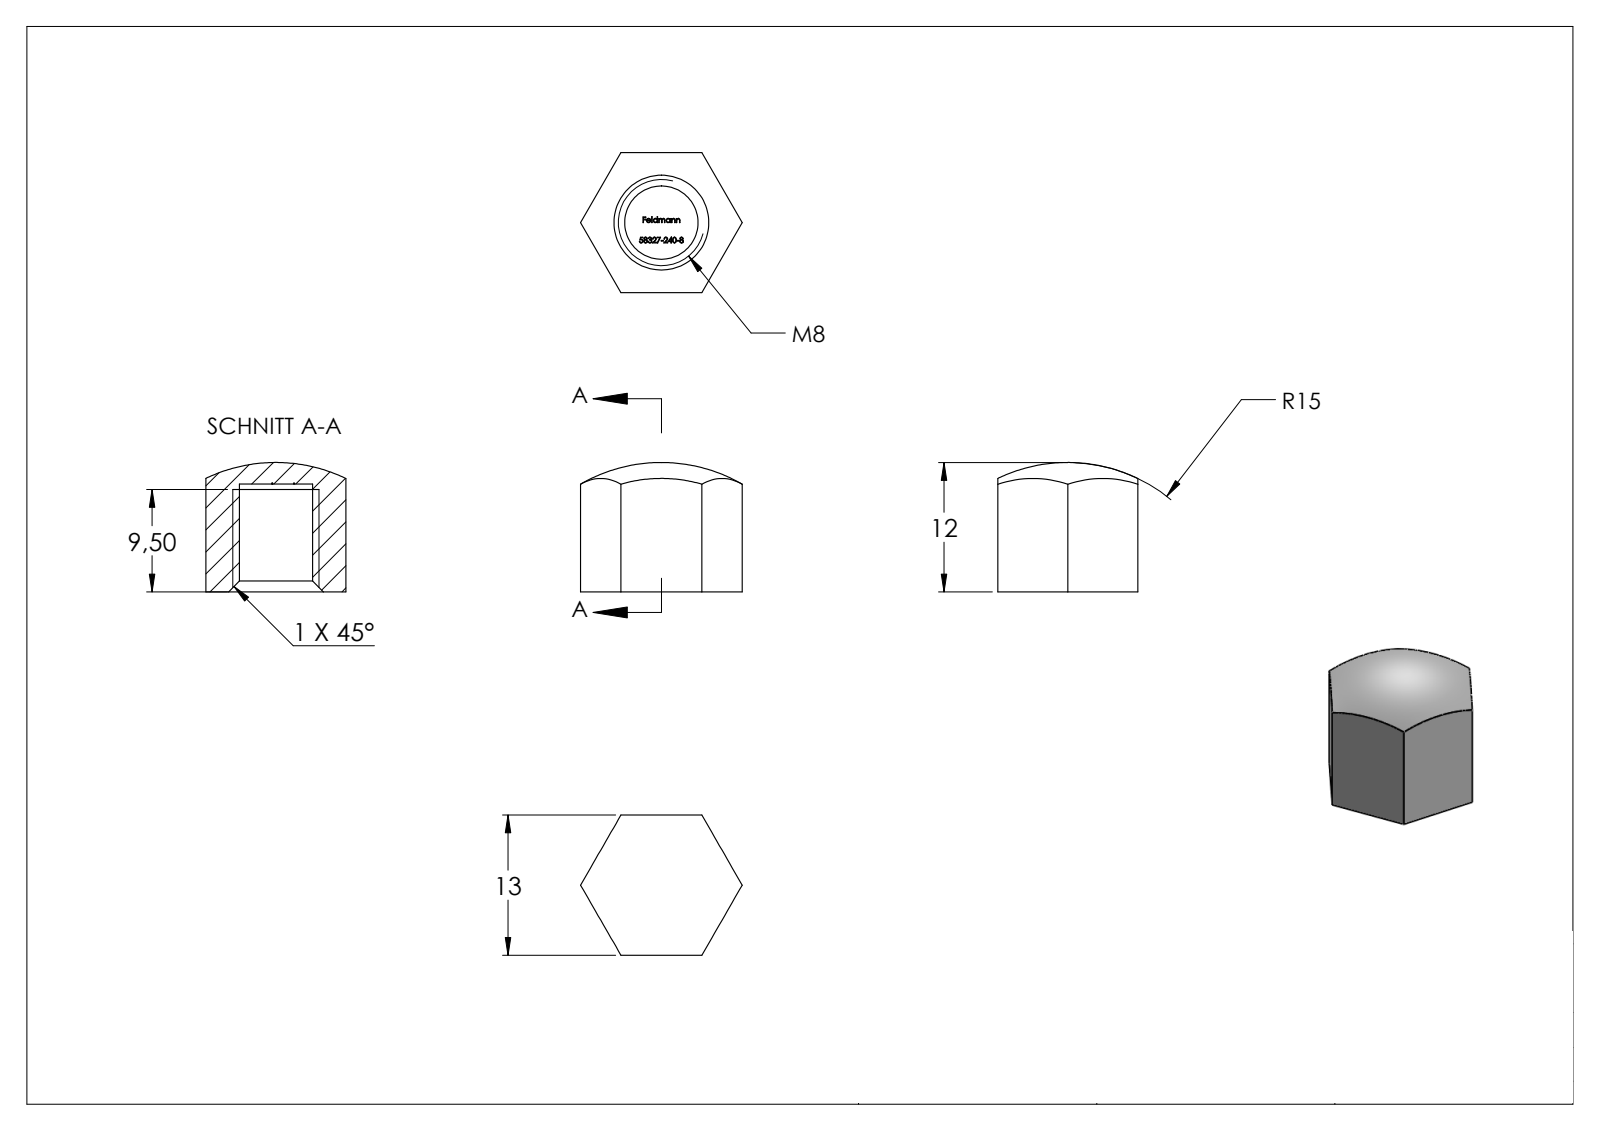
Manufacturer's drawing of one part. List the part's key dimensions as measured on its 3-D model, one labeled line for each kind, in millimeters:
Part name (STEP PRODUCT): 58327-240-8
STEP written by: SolidWorks 2018 (CONFIG_CONTROL_DESIGN)
Units: millimetres
Bodies: 1 solid, 266 faces (138 planar, 1 cylindrical, 127 other)
Overall size (bounding box): 15.01 × 13 × 12
Volume: 1 262 mm³ · Surface area: 974 mm²
Round holes (diameter × count): ⌀6.8 ×1
Main face-to-face distances: 13, 10, 10.1, 1.19, 1.79, 1.35, 1.88, 0.53, 0.55, 1.83
